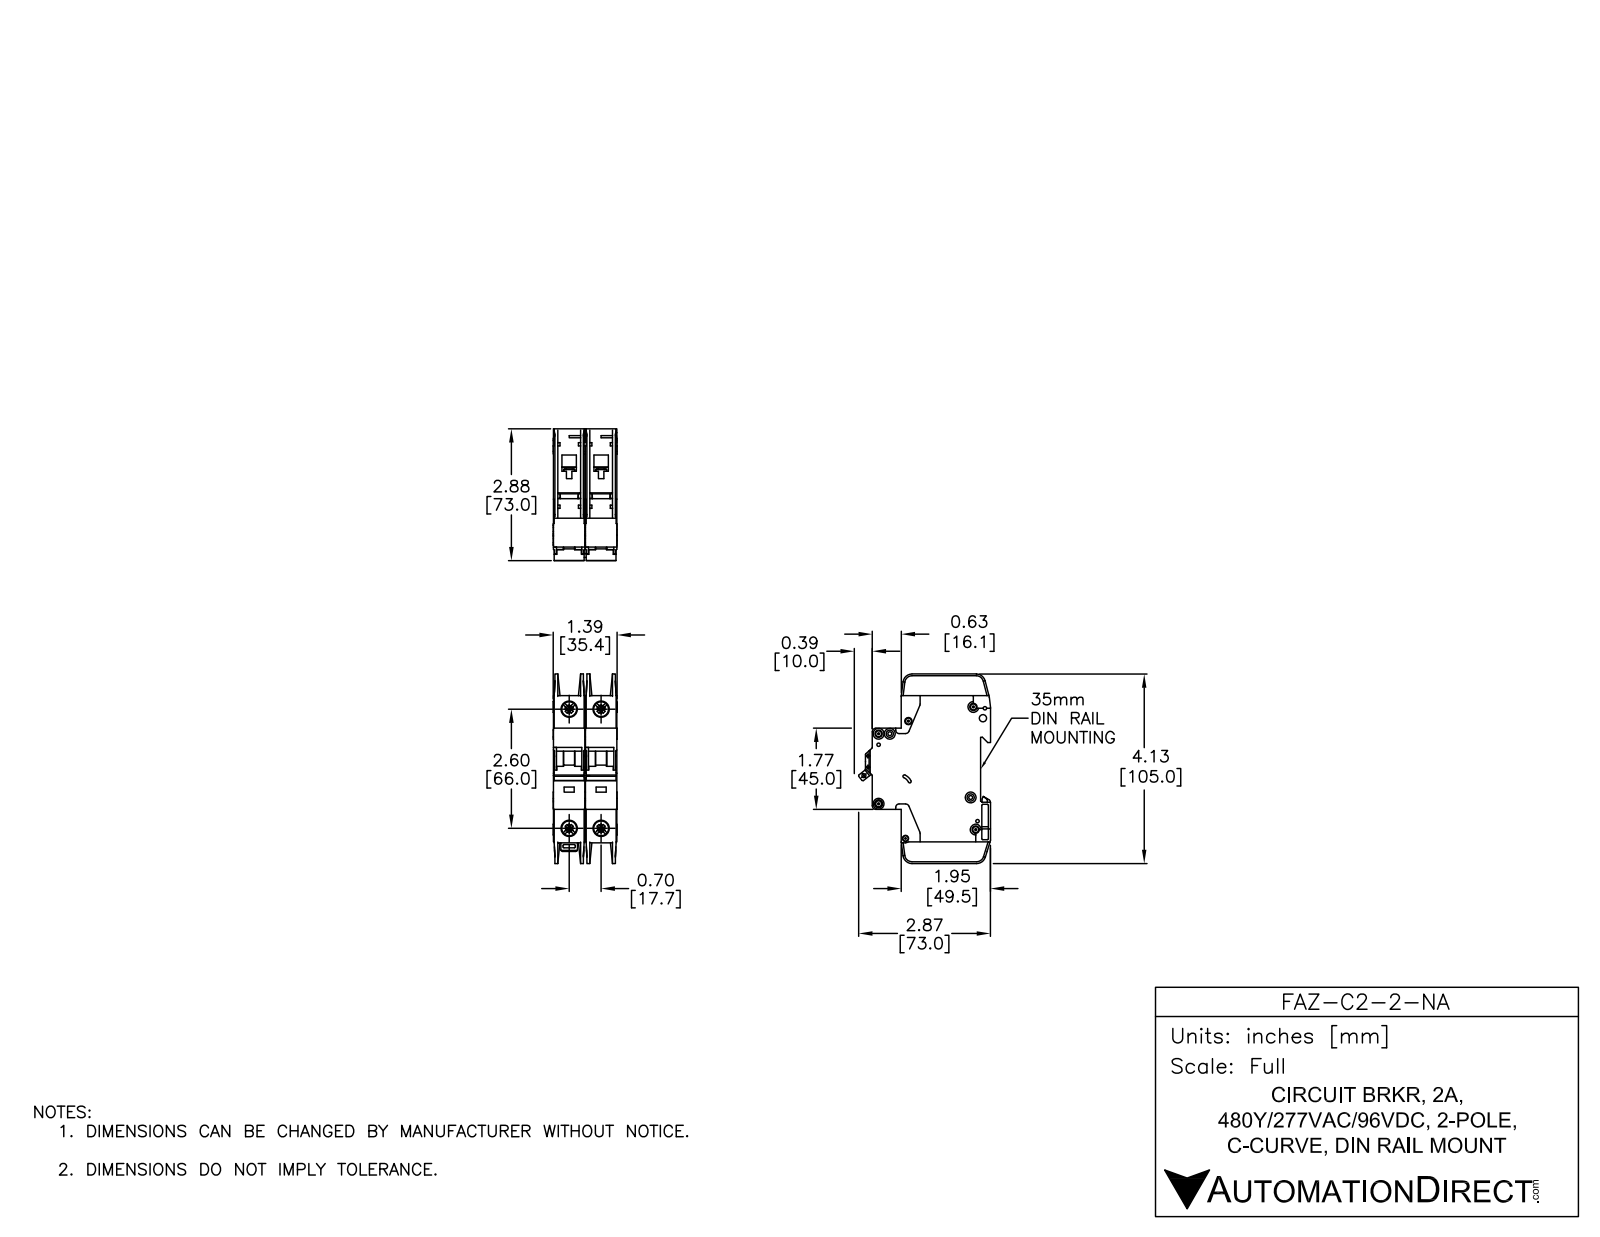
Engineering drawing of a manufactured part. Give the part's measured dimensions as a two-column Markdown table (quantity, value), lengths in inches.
| quantity | value |
| --- | --- |
| part name | FAZ-C2-2-NA |
| STEP written by | SolidWorks 2014 (AUTOMOTIVE_DESIGN) |
| units | inches |
| bodies | 6 solids, 1568 faces (818 planar, 526 cylindrical, 224 other) |
| overall size | 4.134 × 2.876 × 1.394 |
| volume | 9.482 in³ |
| surface area | 76.69 in² |
| round holes (diameter × count) | 0.142 × 7, 0.281 × 4, 0.323 × 4, 0.043 × 2, 0.059 × 2, 0.157 × 2, 0.075 × 1, 0.085 × 1, 0.087 × 1, 0.1 × 1, 0.13 × 1, 0.134 × 1 |
| round bosses / shafts (diameter × count) | 0.236 × 7, 0.098 × 2 |
| partial cylindrical surfaces (radius × count) | 0.01 × 47, 0.02 × 24, 0.039 × 18, 0.079 × 12, 0.197 × 5, 0.071 × 4, 0.157 × 4, 0.008 × 2 |
| main face-to-face distances | 0.697, 0.689, 0.028, 0.593, 0.096, 0.069, 0.62, 0.524, 1.386, 0.669 |
| hole center spacings | 0.244, 0.697, 2.598, 2.69, 0.204, 0.24, 0.322, 0.337 |
